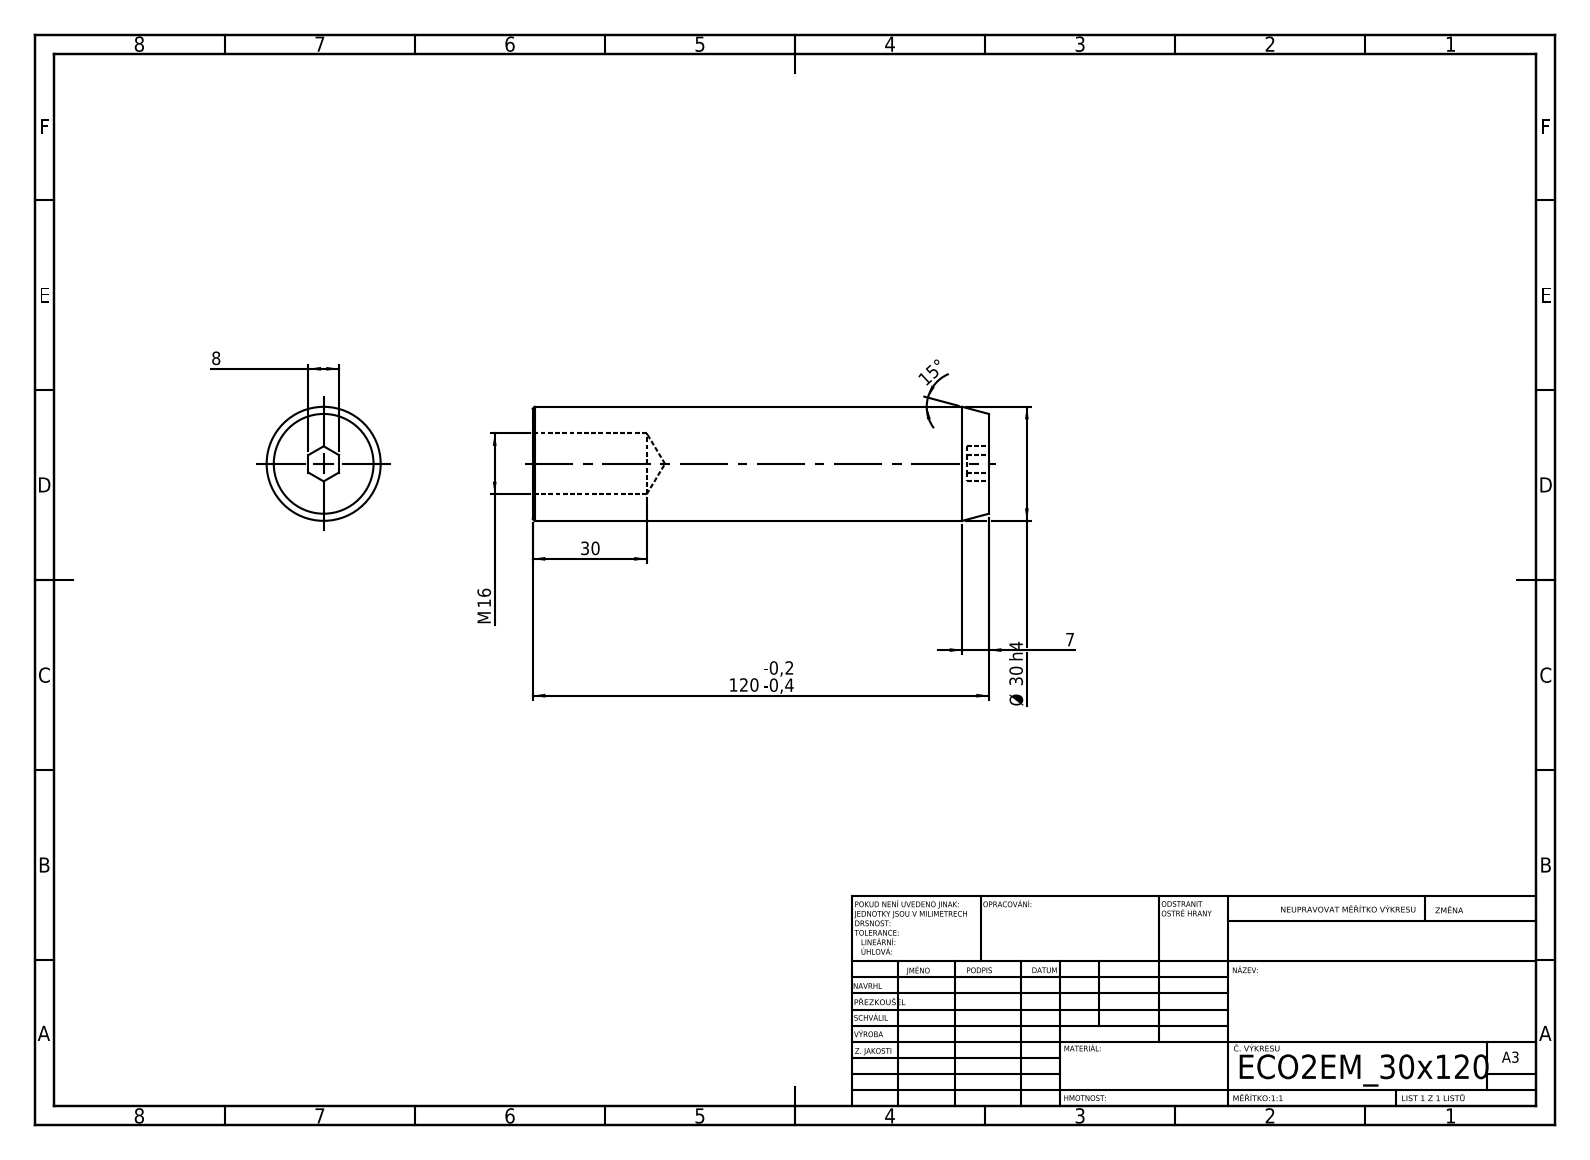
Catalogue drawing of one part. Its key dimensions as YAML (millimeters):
step_written_by: "SolidWorks 2019 (CONFIG_CONTROL_DESIGN)"
units: millimeters
bodies: {solids: 1, faces: 21, planar: 9, cylindrical: 4, other: 8}
overall_size: [120, 30, 30]
volume: 77542
surface_area: 14206
round_holes:
  - {diameter: 16, count: 1}
round_bosses_or_shafts:
  - {diameter: 30, count: 1}
face_to_face_distances: [120, 8, 5.8, 114.2]
